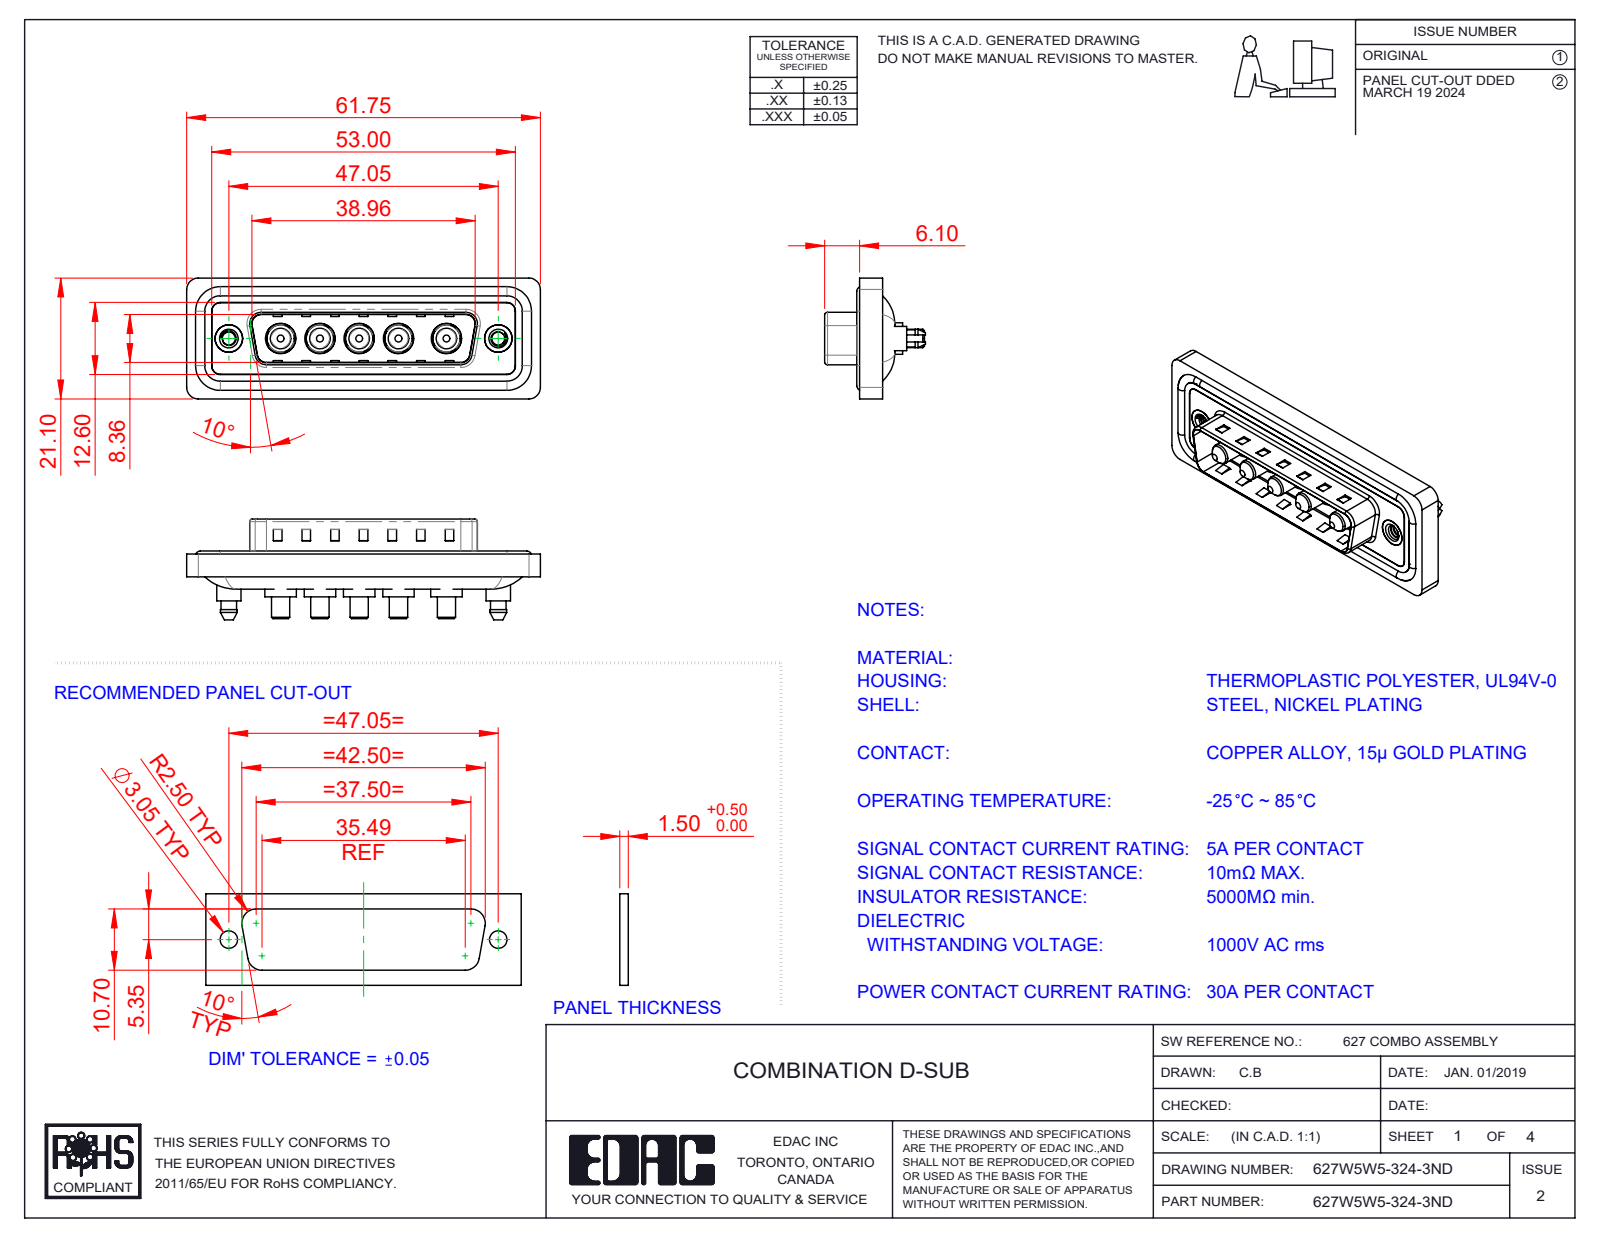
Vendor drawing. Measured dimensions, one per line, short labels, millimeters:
name: 627W5W5-324-3ND; 627Combo Threaded Boardlock_D; 627Combo Shell Rear_25 Contacts; 627Combo Threaded Boardlock_5 (+4 more)
written by: SolidWorks 2023 (CONFIG_CONTROL_DESIGN)
unit: mm
bodies: 17 solids, 736 faces (275 planar, 323 cylindrical, 138 other)
size: 61.75 × 21.1 × 17.6
volume: 7 643 mm³; area: 12 155 mm²
holes: 5× ⌀4.85, 5× ⌀5.3, 2× ⌀2.26, 2× ⌀4, 2× ⌀4.8, 2× ⌀5
bosses: 5× ⌀5.5, 5× ⌀5.2, 5× ⌀4.75, 5× ⌀3.75, 5× ⌀3.6, 5× ⌀3.2, 4× ⌀1.6, 2× ⌀5.4
rounds: 24× R1.5, 18× R2, 10× R1.6, 8× R0.5, 5× R2.1, 4× R0.25, 4× R0.6, 4× R0.65
face distances: 0.4, 1.5, 3.1, 1.1, 0.5, 1.6, 2.9, 0.82, 9.58, 5.65
hole spacings: 6.86, 9.04, 13.73, 38.01, 6.87, 8.37, 8.38, 9.05
